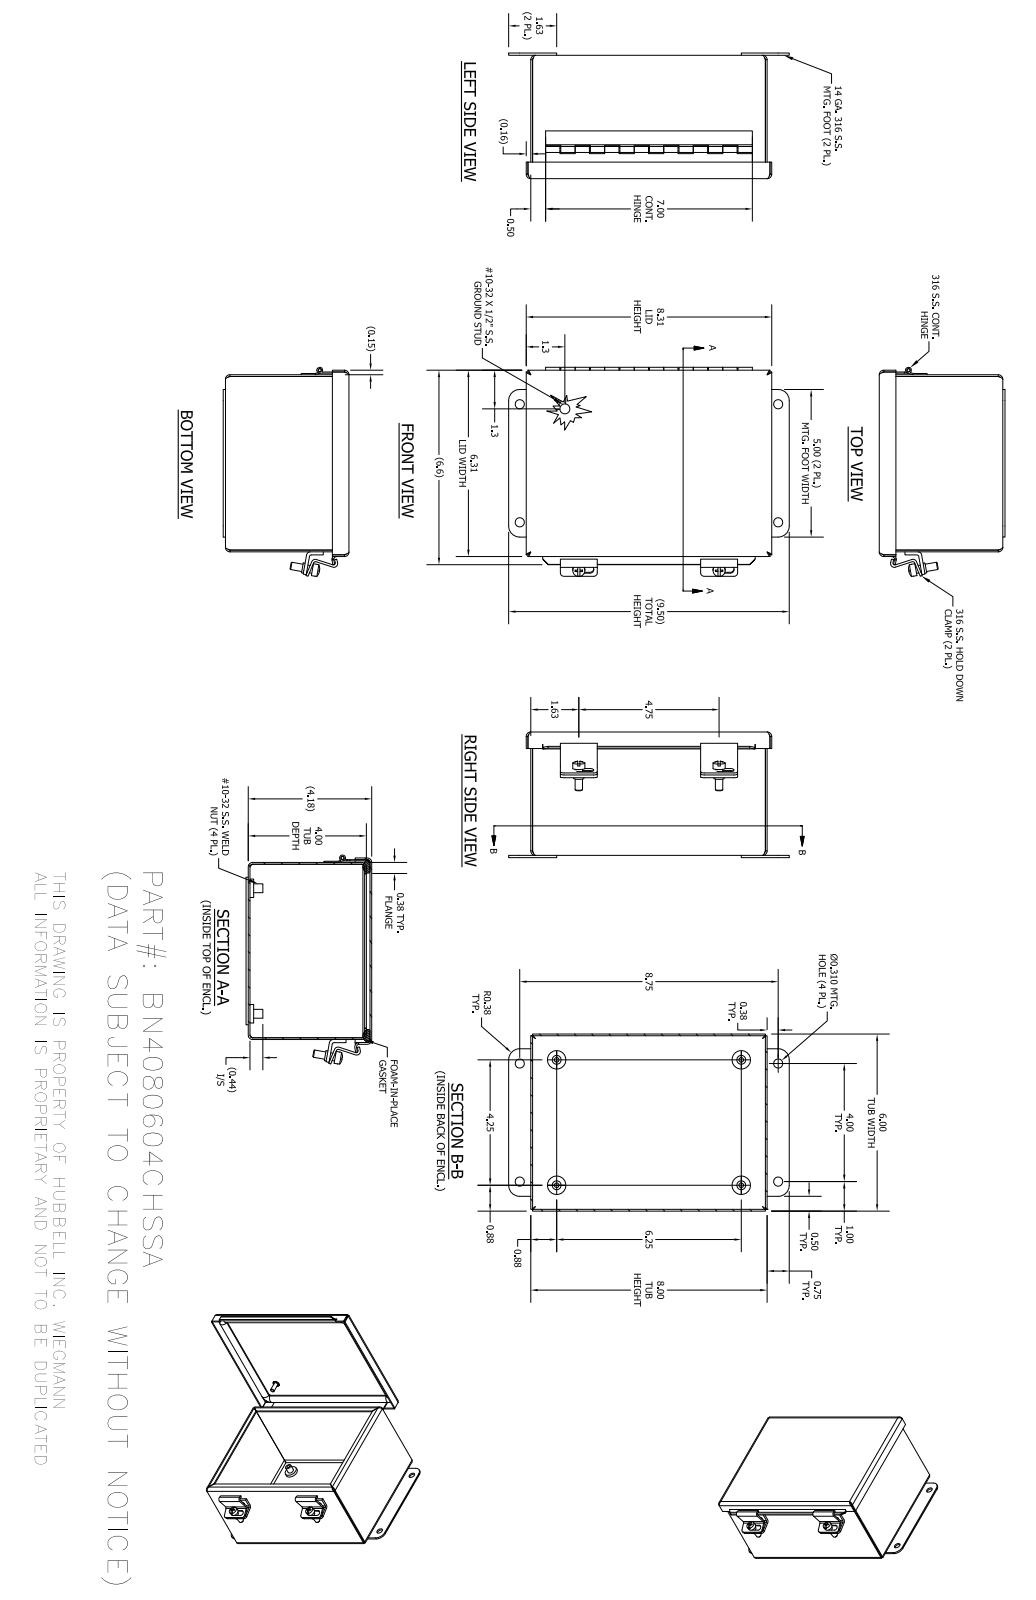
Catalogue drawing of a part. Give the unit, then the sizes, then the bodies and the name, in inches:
Units: inches
Overall size (bounding box): 9.5 × 7.086 × 4.256
Round holes (diameter × count): ⌀0.11 ×4, ⌀0.156 ×4, ⌀0.31 ×4, ⌀0.196 ×2, ⌀0.117 ×1
Round bosses / shafts (diameter × count): ⌀0.625 ×4, ⌀0.3 ×4, ⌀0.409 ×2, ⌀0.344 ×2, ⌀0.25 ×2, ⌀0.337 ×1, ⌀0.2 ×1, ⌀0.19 ×1
Partial cylindrical surfaces — rounded edges, fillets, slot ends (radius × count): R0.094 ×13, R0.153 ×13, R0.066 ×8, R0.125 ×8, R0.133 ×4, R0.228 ×4, R0.375 ×4, R0.063 ×3
Main face-to-face distances: 0.059, 4.122, 5.941, 4.181, 4.063, 7.941, 6, 5.882, 8, 7.882
Hole centre spacings: 1.256, 4.31, 7.501, 8.559, 4, 4.75, 0.75, 4.25
Volume: 18.44 in³ · Surface area: 579.1 in²
Bodies: 19 solids, 428 faces (232 planar, 129 cylindrical, 67 other)
Part name (STEP PRODUCT): B_080604_SSABKP; 328145LH; 328145P; 328145TH (+8 more)
STEP written by: Autodesk Inventor 2016 (AUTOMOTIVE_DESIGN)
